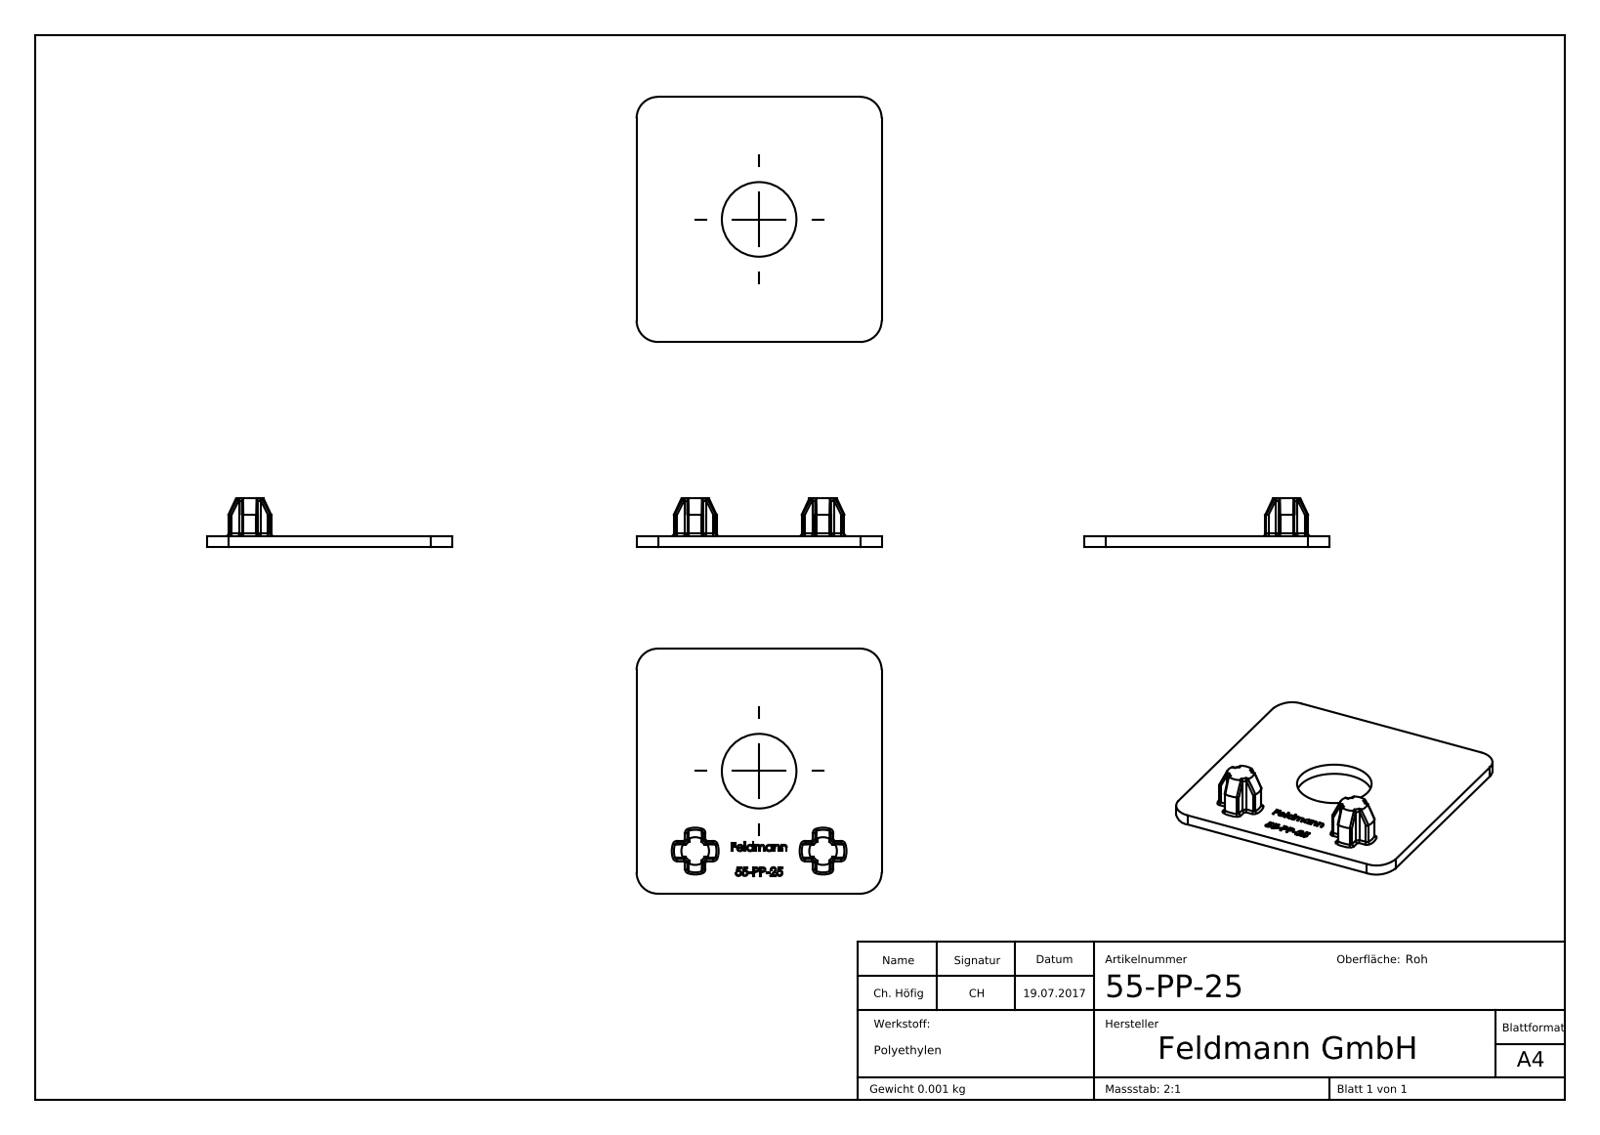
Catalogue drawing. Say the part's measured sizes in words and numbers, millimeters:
The part is named "55-PP-25". Its 3-D file was written by "SolidWorks 2015 (CONFIG_CONTROL_DESIGN)". It is 1 solid with 377 faces: 147 planar, 72 cylindrical and 158 other. Overall it measures 23 by 23 by 4.5 millimeters. Its volume is 548 cubic millimeters and its surface area 1 170 square millimeters. Round holes: 1 of diameter 7. Partial cylindrical surfaces (rounded edges, fillets, slot ends): 28 of radius 0.2, 6 of radius 2, 2 of radius 1.25. The main face-to-face distances are 1, 23, 4.75, 18.25, 1.5, 4.5, 3.5, 6.25, 16.75, 12.
